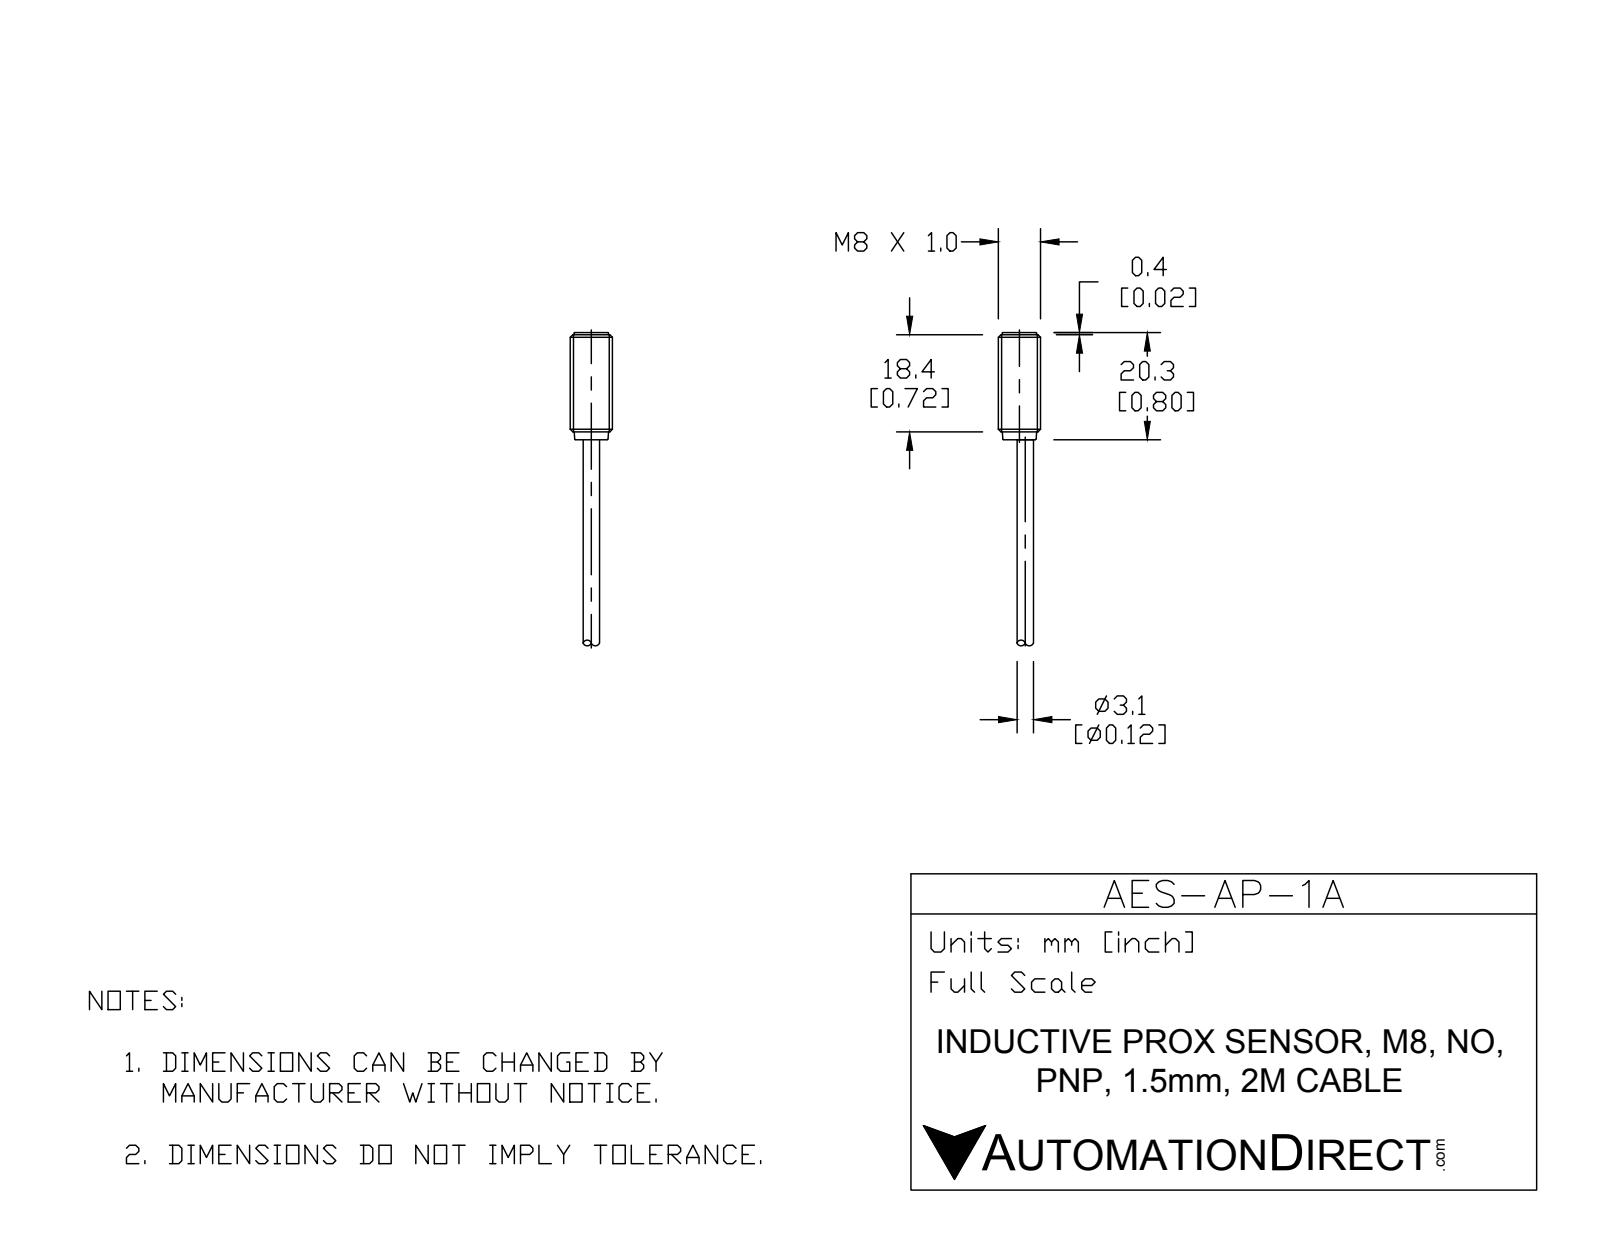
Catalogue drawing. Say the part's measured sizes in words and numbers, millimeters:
The part is named "AES-AP-1A". Its 3-D file was written by "SolidWorks 2015 (CONFIG_CONTROL_DESIGN)". It is 1 solid with 21 faces: 5 planar, 6 cylindrical and 10 other. Overall it measures 69.9 by 8 by 8 millimeters. Its volume is 1 335 cubic millimeters and its surface area 1 054 square millimeters. Round bosses or shafts: 1 of diameter 8, 1 of diameter 6.5, 1 of diameter 3.1. The main face-to-face distances are 19.9, 50, 69.9, 69.5, 19.5, 0.4, 51.5, 1.5, 18, 18.4.
